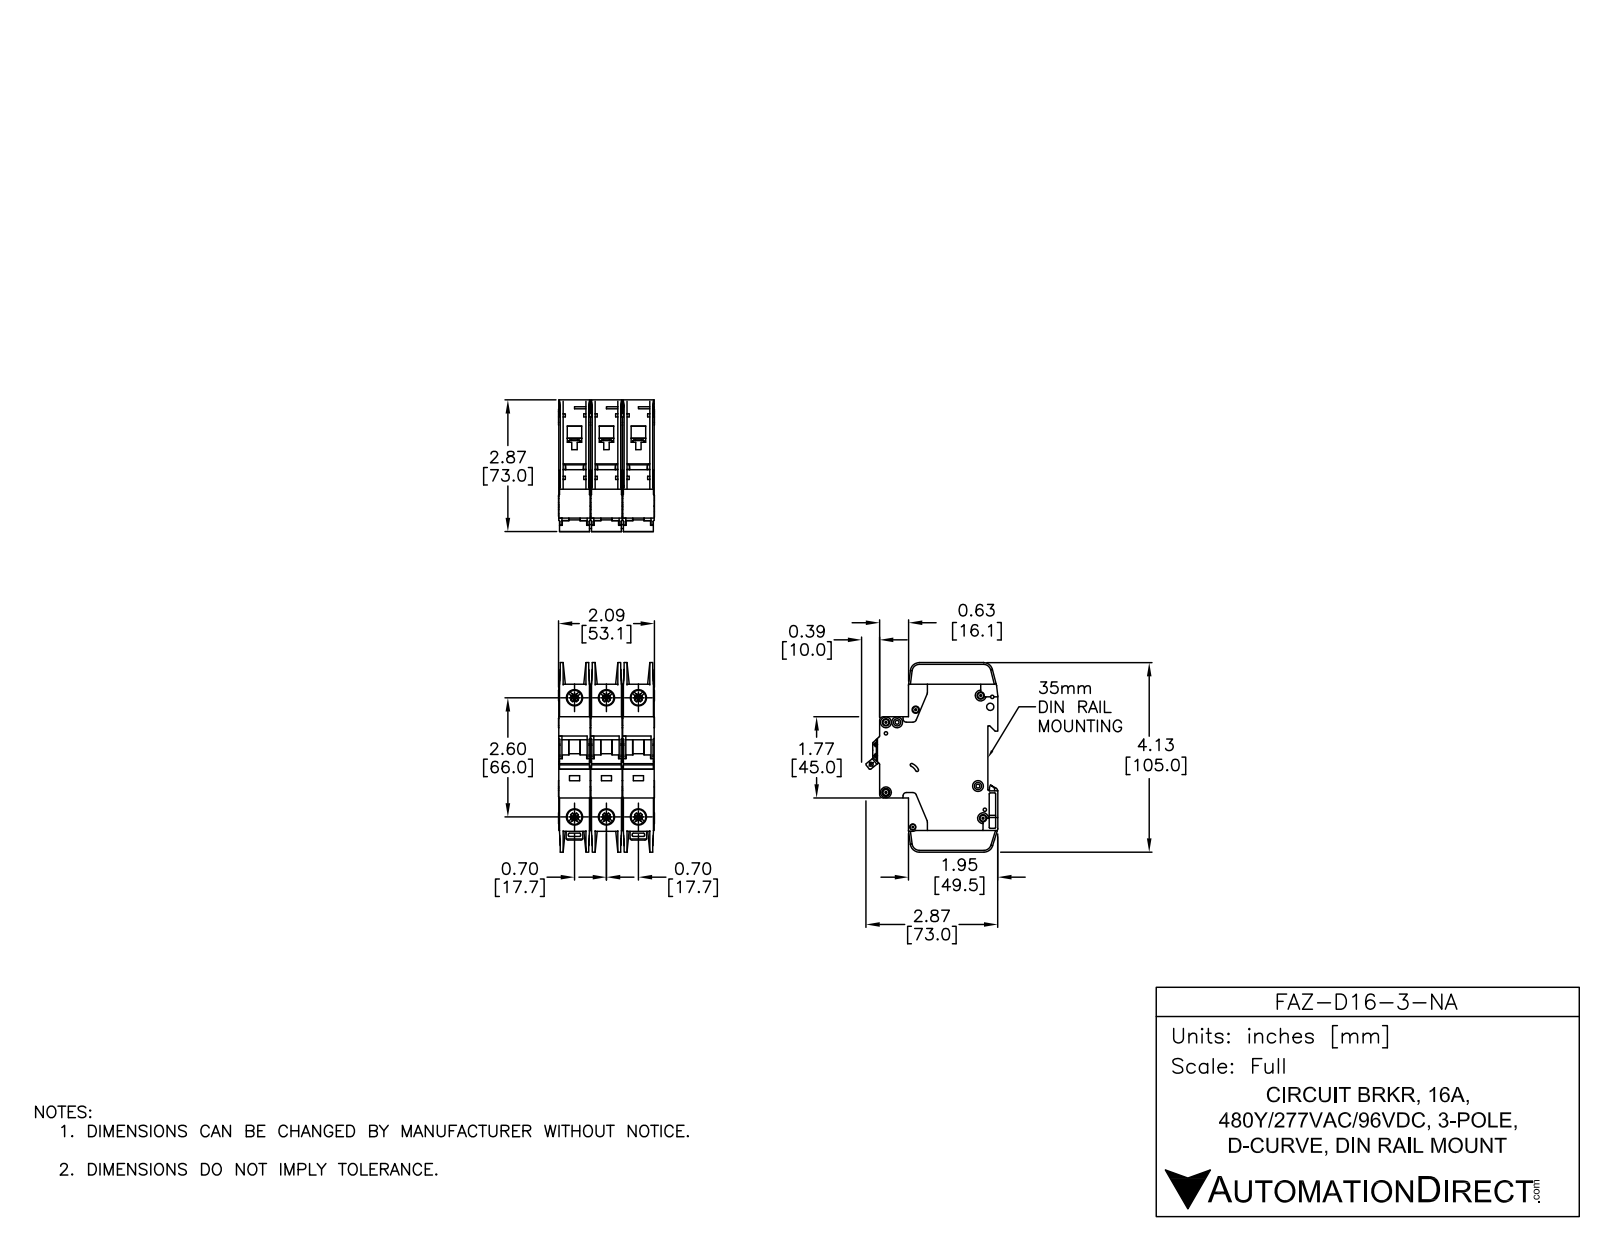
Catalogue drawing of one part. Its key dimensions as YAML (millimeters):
part_name: "FAZ-D16-3-NA"
step_written_by: "SolidWorks 2014 (AUTOMOTIVE_DESIGN)"
units: millimeters
bodies: {solids: 9, faces: 2352, planar: 1227, cylindrical: 789, other: 336}
overall_size: [105, 73.04, 53.1]
volume: 233085
surface_area: 74219
round_holes:
  - {diameter: 3.6, count: 7}
  - {diameter: 7.15, count: 6}
  - {diameter: 8.2, count: 6}
  - {diameter: 1.09, count: 2}
  - {diameter: 1.5, count: 2}
  - {diameter: 4, count: 2}
  - {diameter: 1.9, count: 1}
  - {diameter: 2.15, count: 1}
  - {diameter: 2.2, count: 1}
  - {diameter: 2.55, count: 1}
  - {diameter: 3.3, count: 1}
  - {diameter: 3.4, count: 1}
round_bosses_or_shafts:
  - {diameter: 6, count: 7}
  - {diameter: 2.5, count: 3}
partial_cylinders:
  - {radius: 0.25, count: 65}
  - {radius: 0.5, count: 30}
  - {radius: 1, count: 26}
  - {radius: 2, count: 14}
  - {radius: 1.8, count: 5}
  - {radius: 5, count: 5}
  - {radius: 4, count: 4}
  - {radius: 0.2, count: 2}
face_to_face_distances: [17.7, 35.4, 17.5, 35.2, 0.7, 15.05, 2.45, 1.75, 15.75, 13.3]
hole_center_spacings: [17.7, 68.33, 66, 6.2, 35.4, 74.89, 5.19, 6.1]
